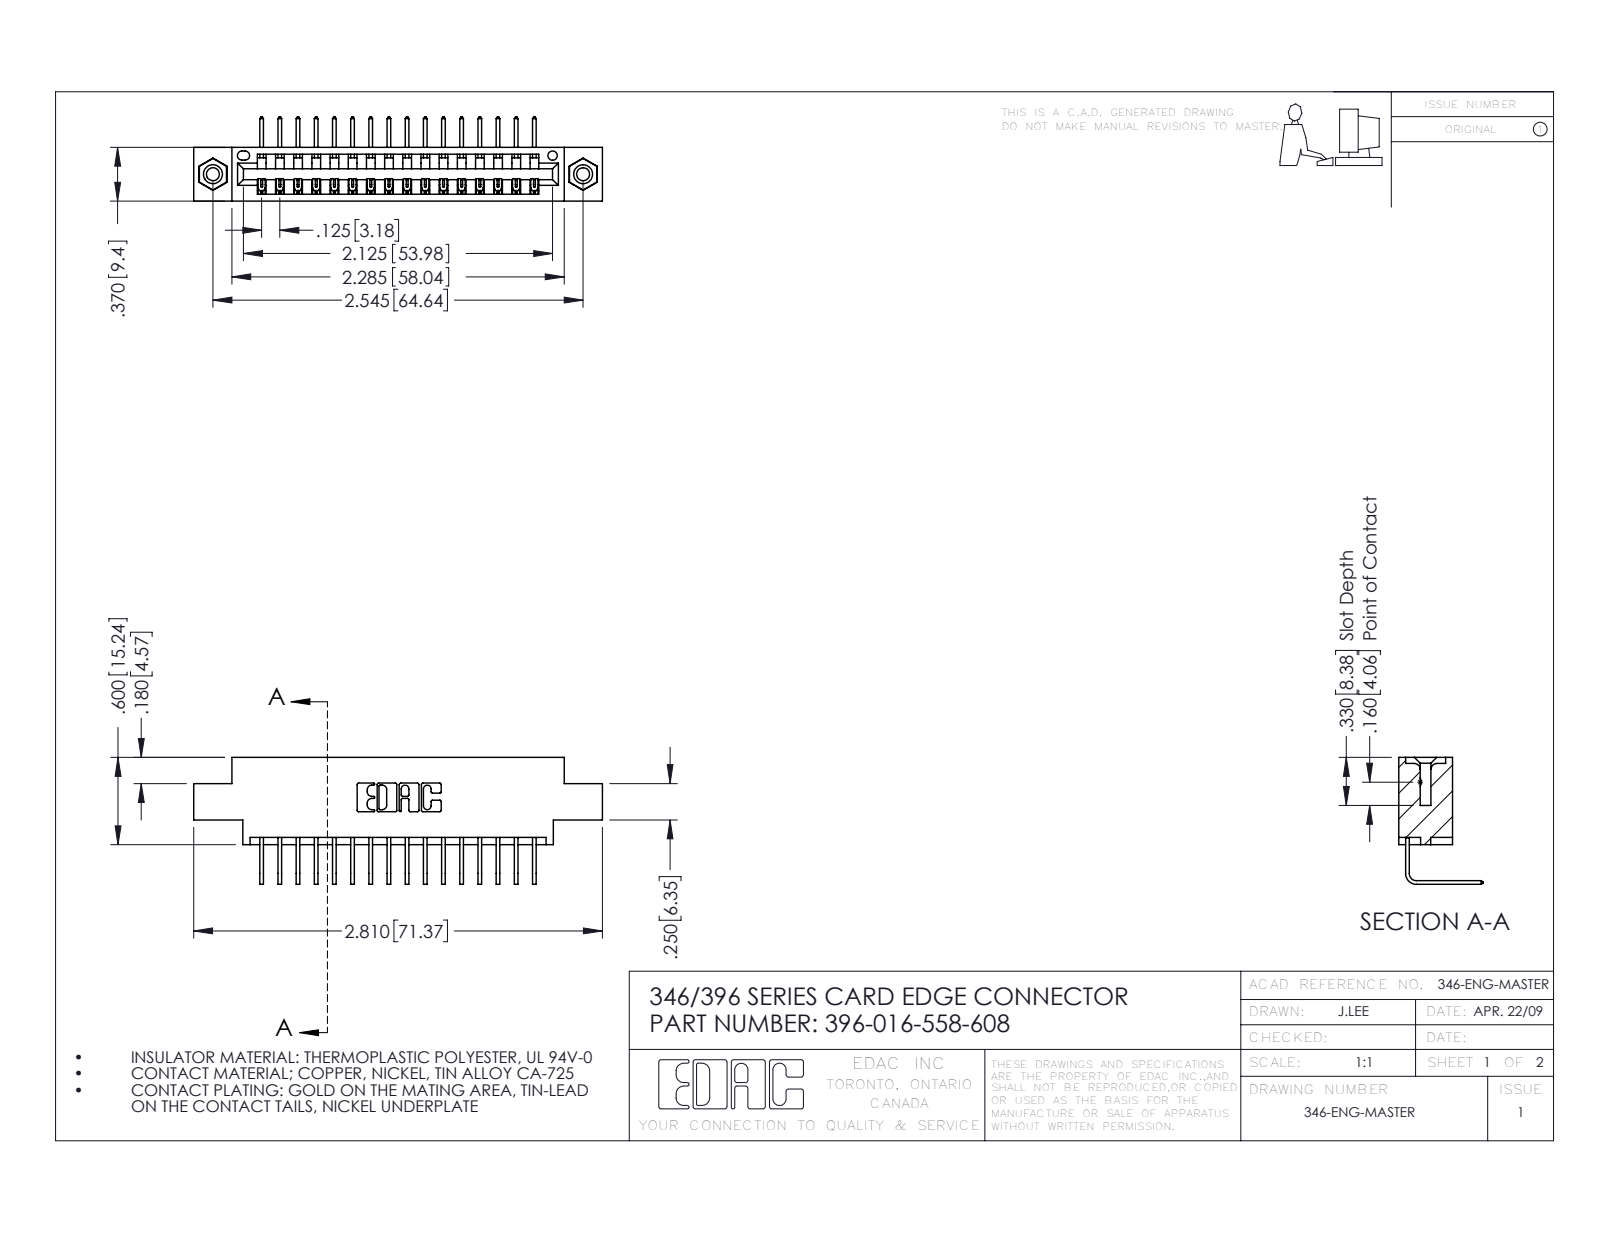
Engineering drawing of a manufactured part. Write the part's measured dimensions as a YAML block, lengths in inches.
part_name: "345-250-001_345-250-003-102; 346 Part_0.170 Offset - 0.156 Dia-TI; 345-292-001_558 Tail - 2; 396-016-558-608"
step_written_by: "SolidWorks 2016 (CONFIG_CONTROL_DESIGN)"
units: inches
bodies: {solids: 19, faces: 1146, planar: 784, cylindrical: 346, other: 16}
overall_size: [2.81, 0.873, 0.58]
volume: 0.399
surface_area: 13.02
round_holes:
  - {diameter: 0.089, count: 2}
  - {diameter: 0.125, count: 2}
  - {diameter: 0.156, count: 2}
  - {diameter: 0.064, count: 1}
round_bosses_or_shafts:
  - {diameter: 0.155, count: 2}
partial_cylinders:
  - {radius: 0.006, count: 32}
  - {radius: 0.01, count: 22}
  - {radius: 0.007, count: 6}
  - {radius: 0.031, count: 6}
  - {radius: 0.026, count: 3}
  - {radius: 0.031, count: 2}
  - {radius: 0.04, count: 2}
  - {radius: 0.014, count: 1}
face_to_face_distances: [0.322, 0.048, 0.37, 0.25, 0.298, 0.025, 0.222, 0.072, 0.148, 0.1]
hole_center_spacings: [0.246, 2.338, 2.545]
